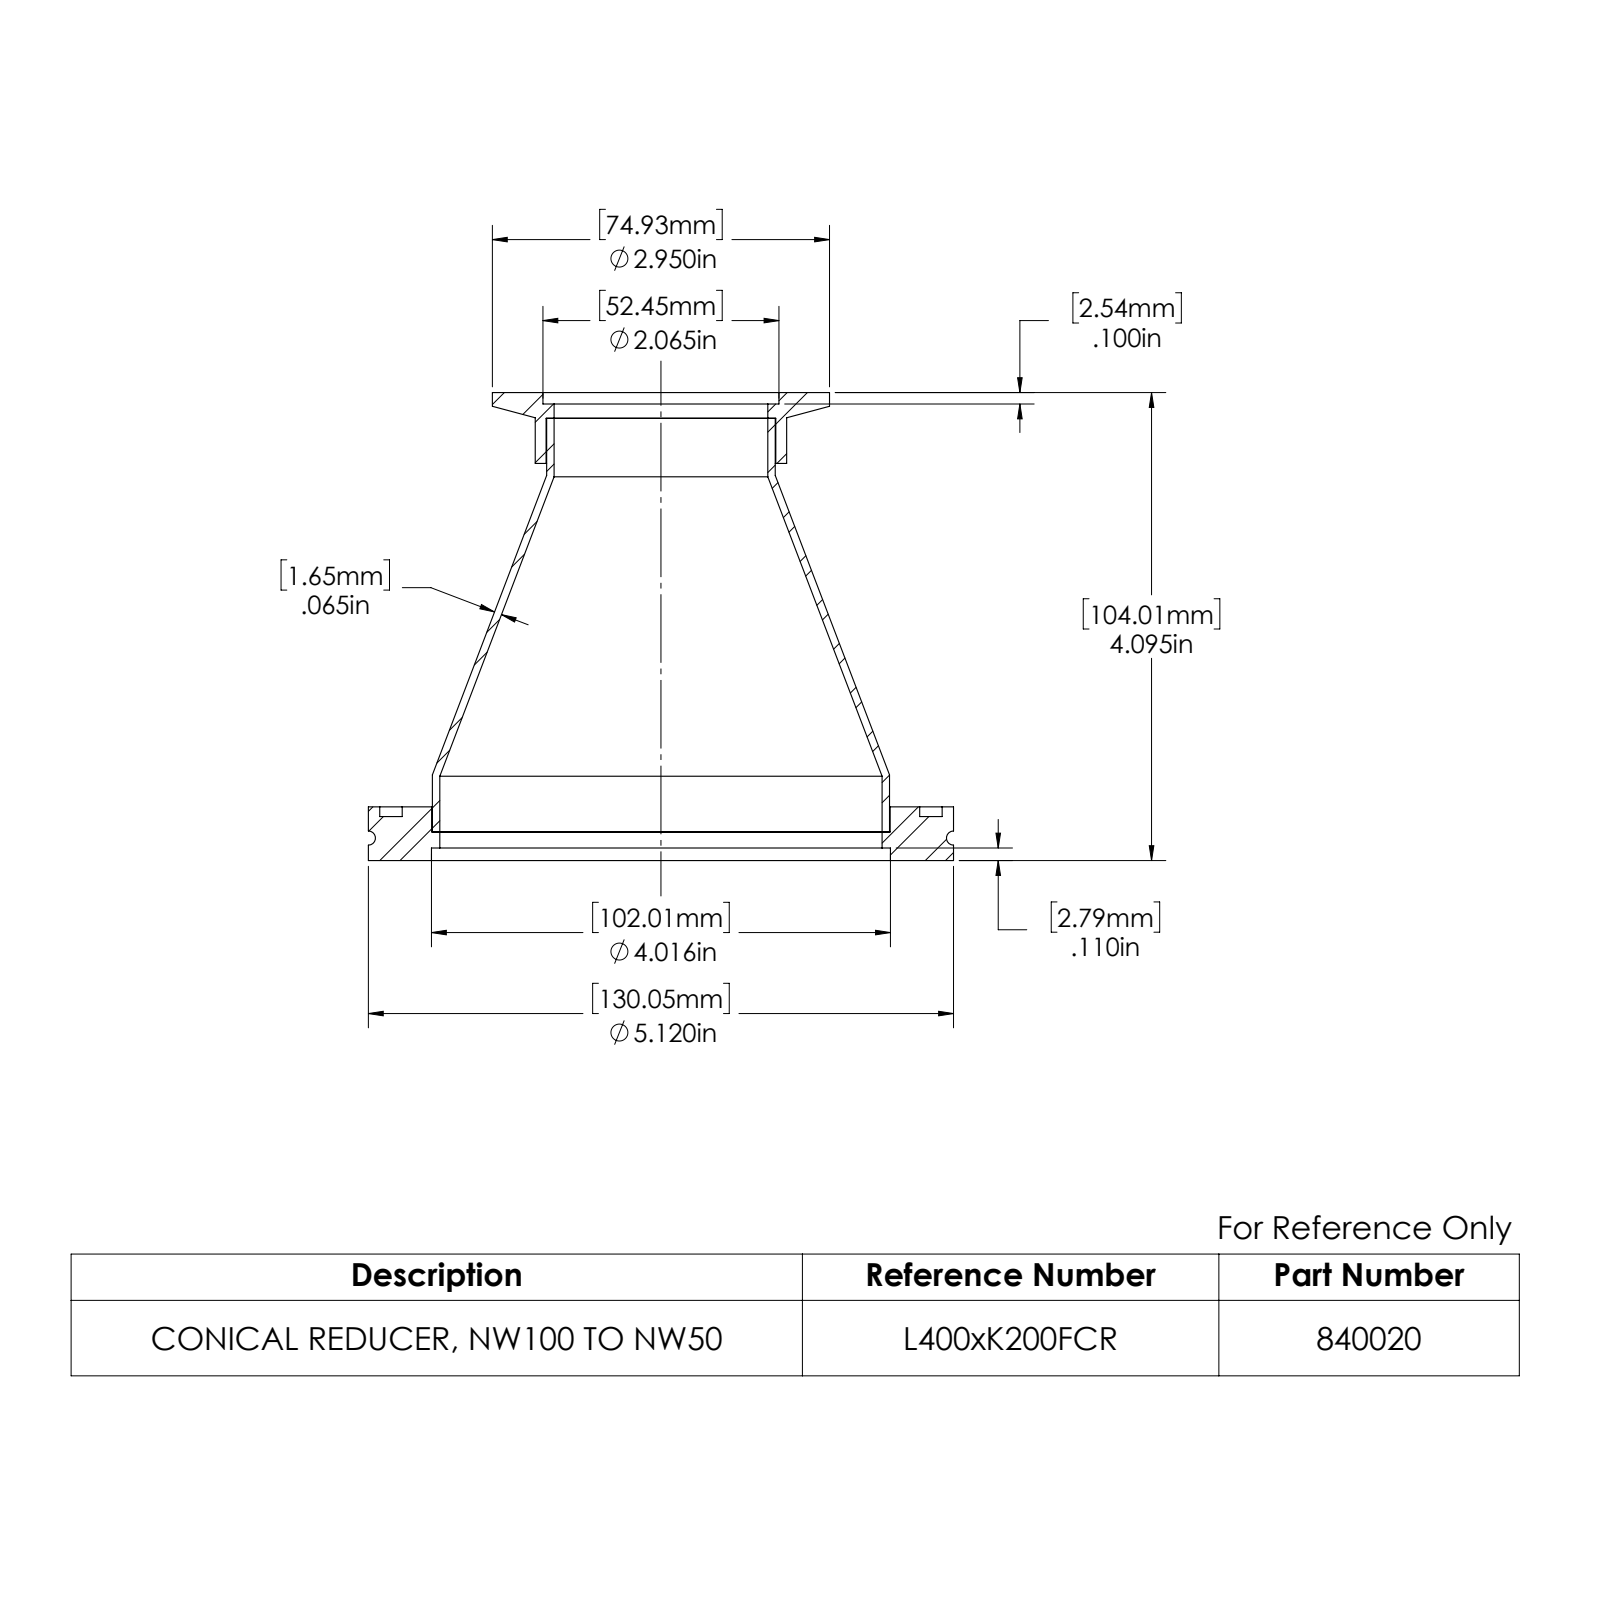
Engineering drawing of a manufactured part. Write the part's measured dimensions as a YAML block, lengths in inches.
part_name: "SUB1; 813001; 713004; 840020"
step_written_by: "SolidWorks 2022 (AUTOMOTIVE_DESIGN)"
units: inches
bodies: {solids: 3, faces: 54, planar: 12, cylindrical: 32, other: 10}
overall_size: [5.12, 5.12, 4.125]
volume: 6.743
surface_area: 122.5
round_holes:
  - {diameter: 1.87, count: 1}
  - {diameter: 2.01, count: 1}
  - {diameter: 2.065, count: 1}
  - {diameter: 3.87, count: 1}
  - {diameter: 4.01, count: 1}
  - {diameter: 4.016, count: 1}
  - {diameter: 4.921, count: 1}
round_bosses_or_shafts:
  - {diameter: 5.12, count: 1}
  - {diameter: 4.528, count: 1}
  - {diameter: 4, count: 1}
  - {diameter: 2.95, count: 1}
  - {diameter: 2.2, count: 1}
  - {diameter: 2, count: 1}
face_to_face_distances: [0.47, 4.125, 3.655, 0.385, 0.085, 3.74, 0.25, 0.135, 0.22, 3.875]
